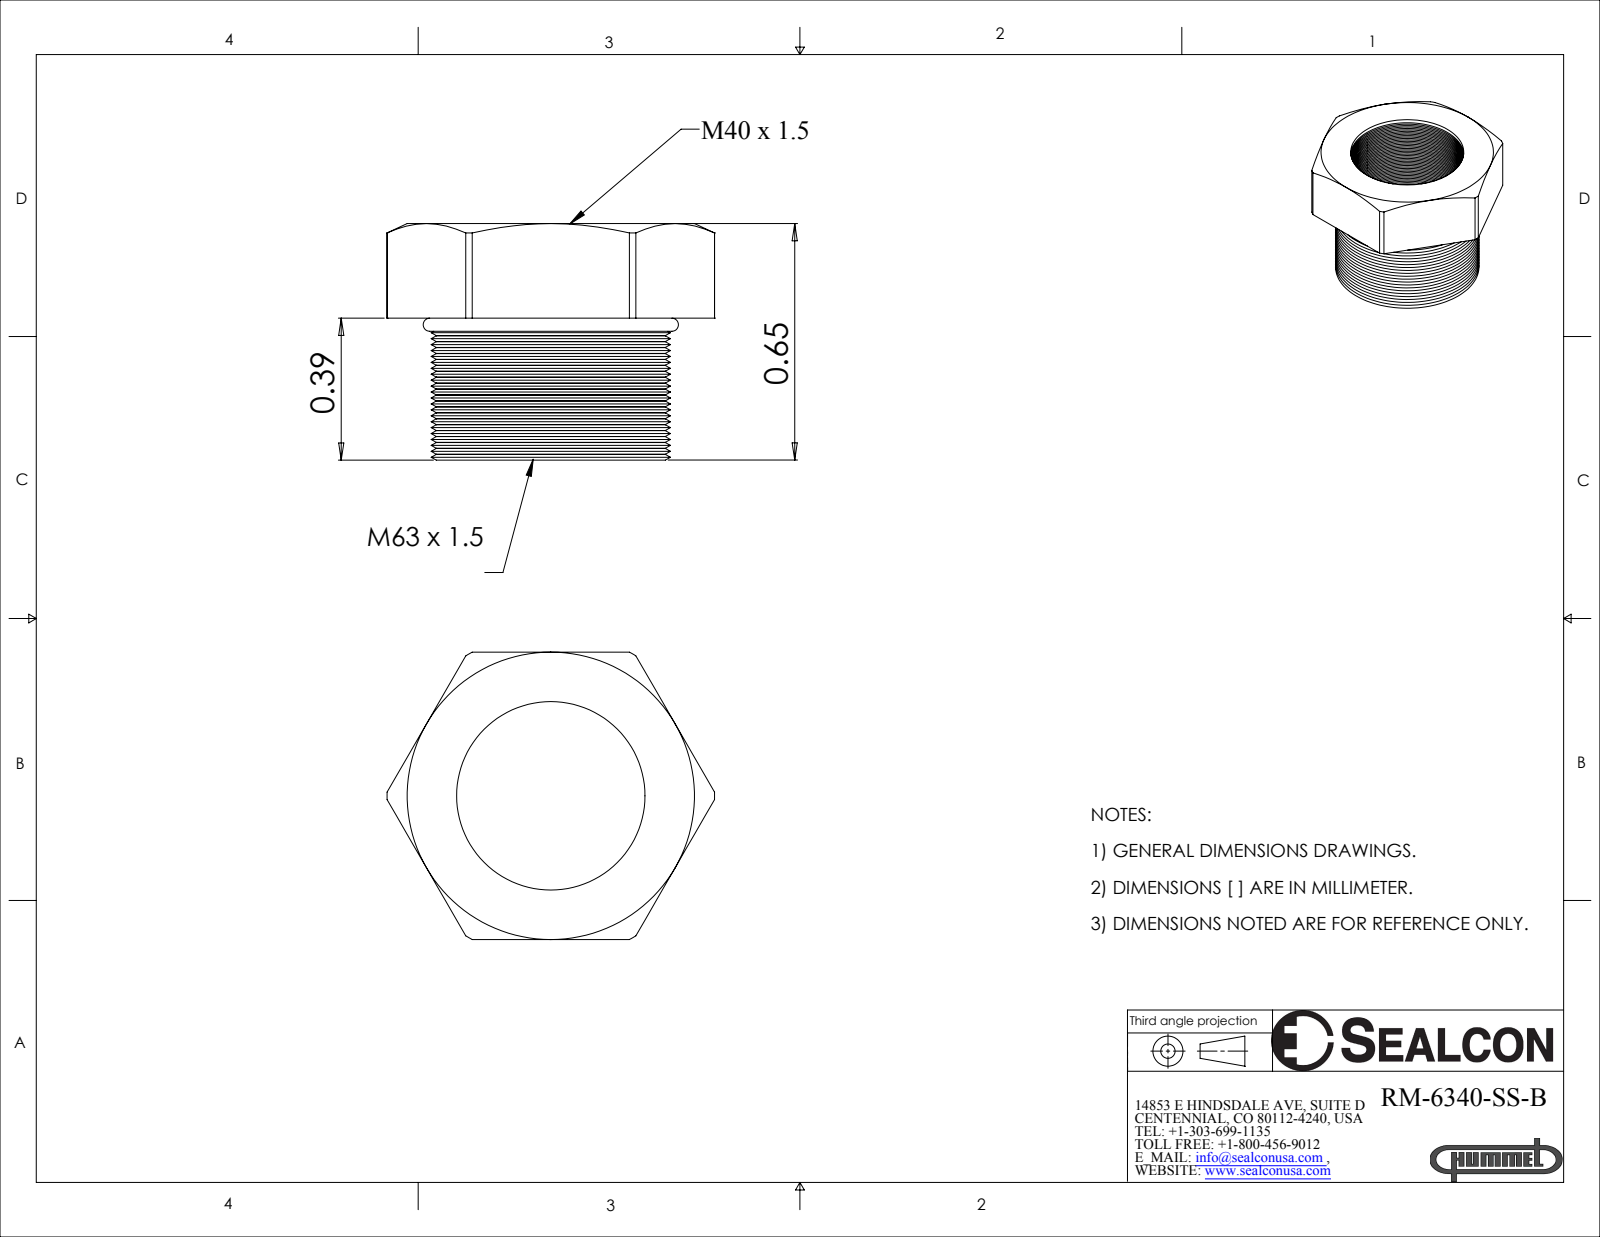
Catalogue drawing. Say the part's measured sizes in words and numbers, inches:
The part is named "RM-6340-SS-B". Its 3-D file was written by "SolidWorks 2008 (CONFIG_CONTROL_DESIGN)". It is 2 solids with 403 faces: 9 planar, 135 cylindrical and 259 other. Overall it measures 0.901 by 0.79 by 0.65 inches. Its volume is 0.129 cubic inches and its surface area 5.229 square inches. Round holes: 1 of diameter 0.518. Round bosses or shafts: 1 of diameter 0.63. Partial cylindrical surfaces (rounded edges, fillets, slot ends): 1 of radius 0.45. The main face-to-face distances are 0.79, 0.26, 0.39, 0.65.
